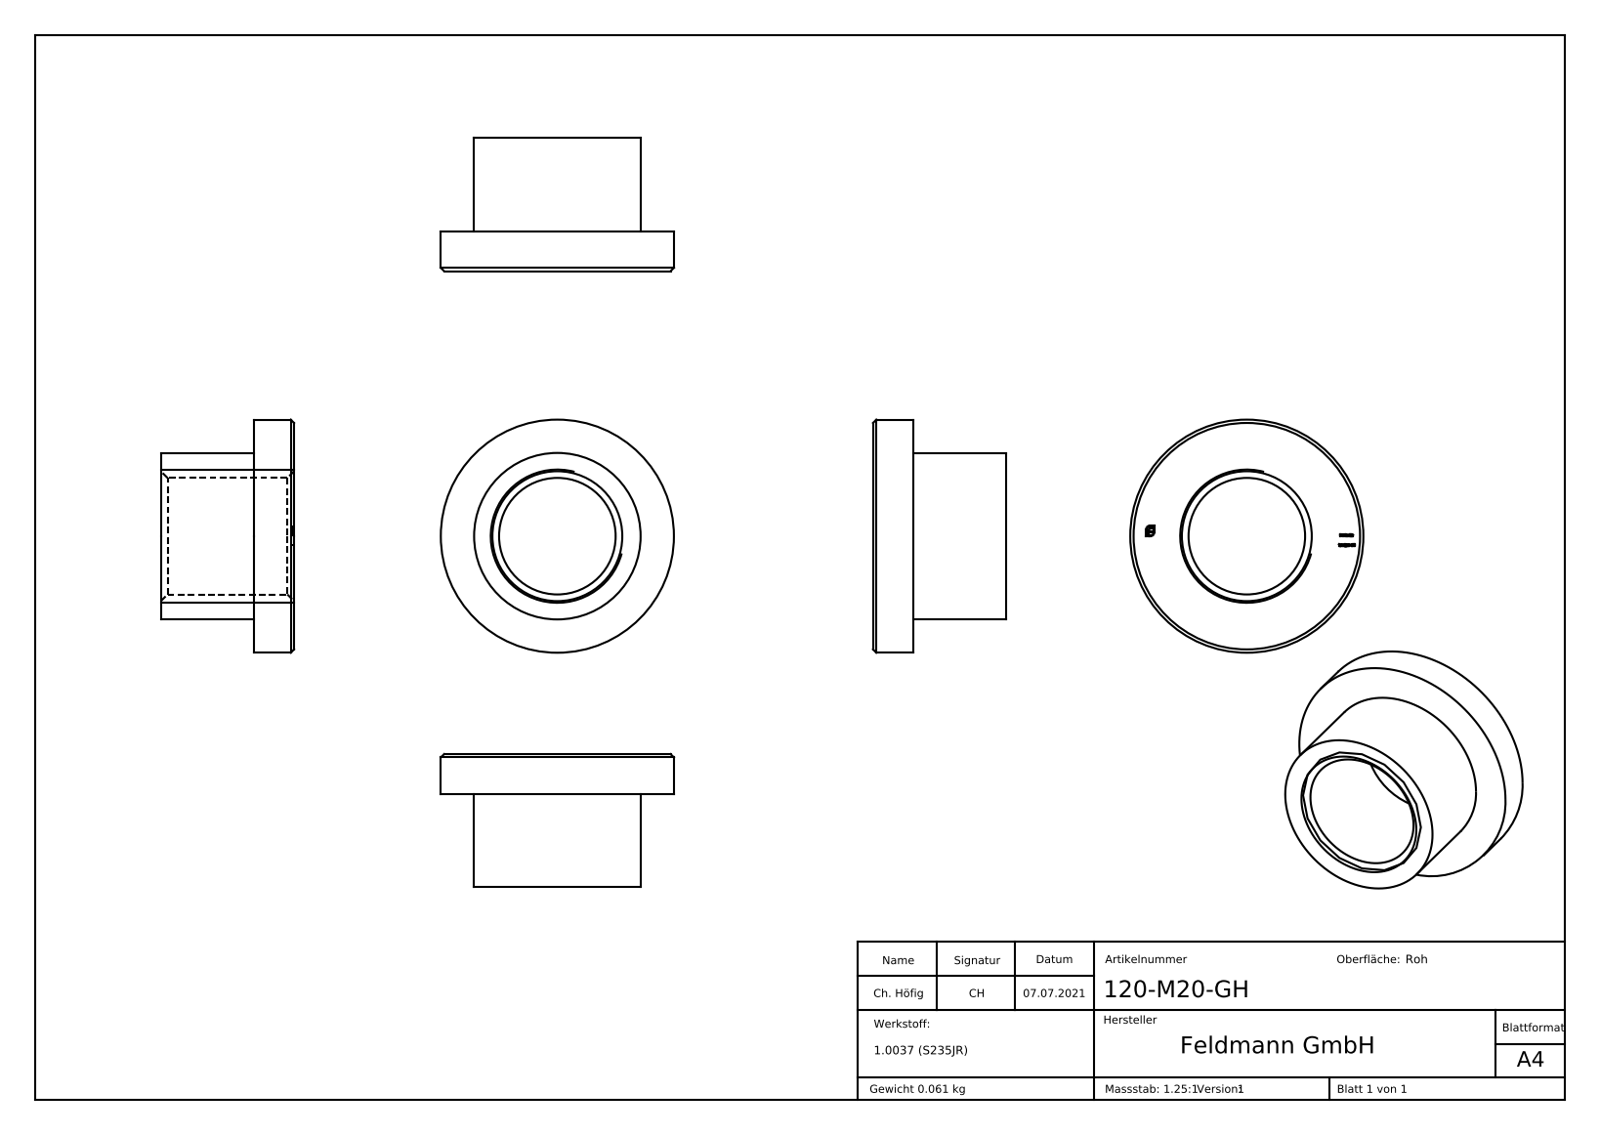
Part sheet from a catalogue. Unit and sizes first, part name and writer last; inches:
Units: inches
Overall size (bounding box): 1.378 × 1.378 × 0.787
Round holes (diameter × count): ⌀0.689 ×1
Round bosses / shafts (diameter × count): ⌀1.378 ×1, ⌀0.984 ×1
Main face-to-face distances: 0.236, 0.787, 0.551, 0.232, 0.783, 0.059, 0.058, 0.019, 0.057, 0.039
Volume: 0.474 in³ · Surface area: 6.527 in²
Bodies: 1 solid, 277 faces (158 planar, 6 cylindrical, 113 other)
Part name (STEP PRODUCT): 120-M20-GH
STEP written by: SolidWorks 2018 (CONFIG_CONTROL_DESIGN)
